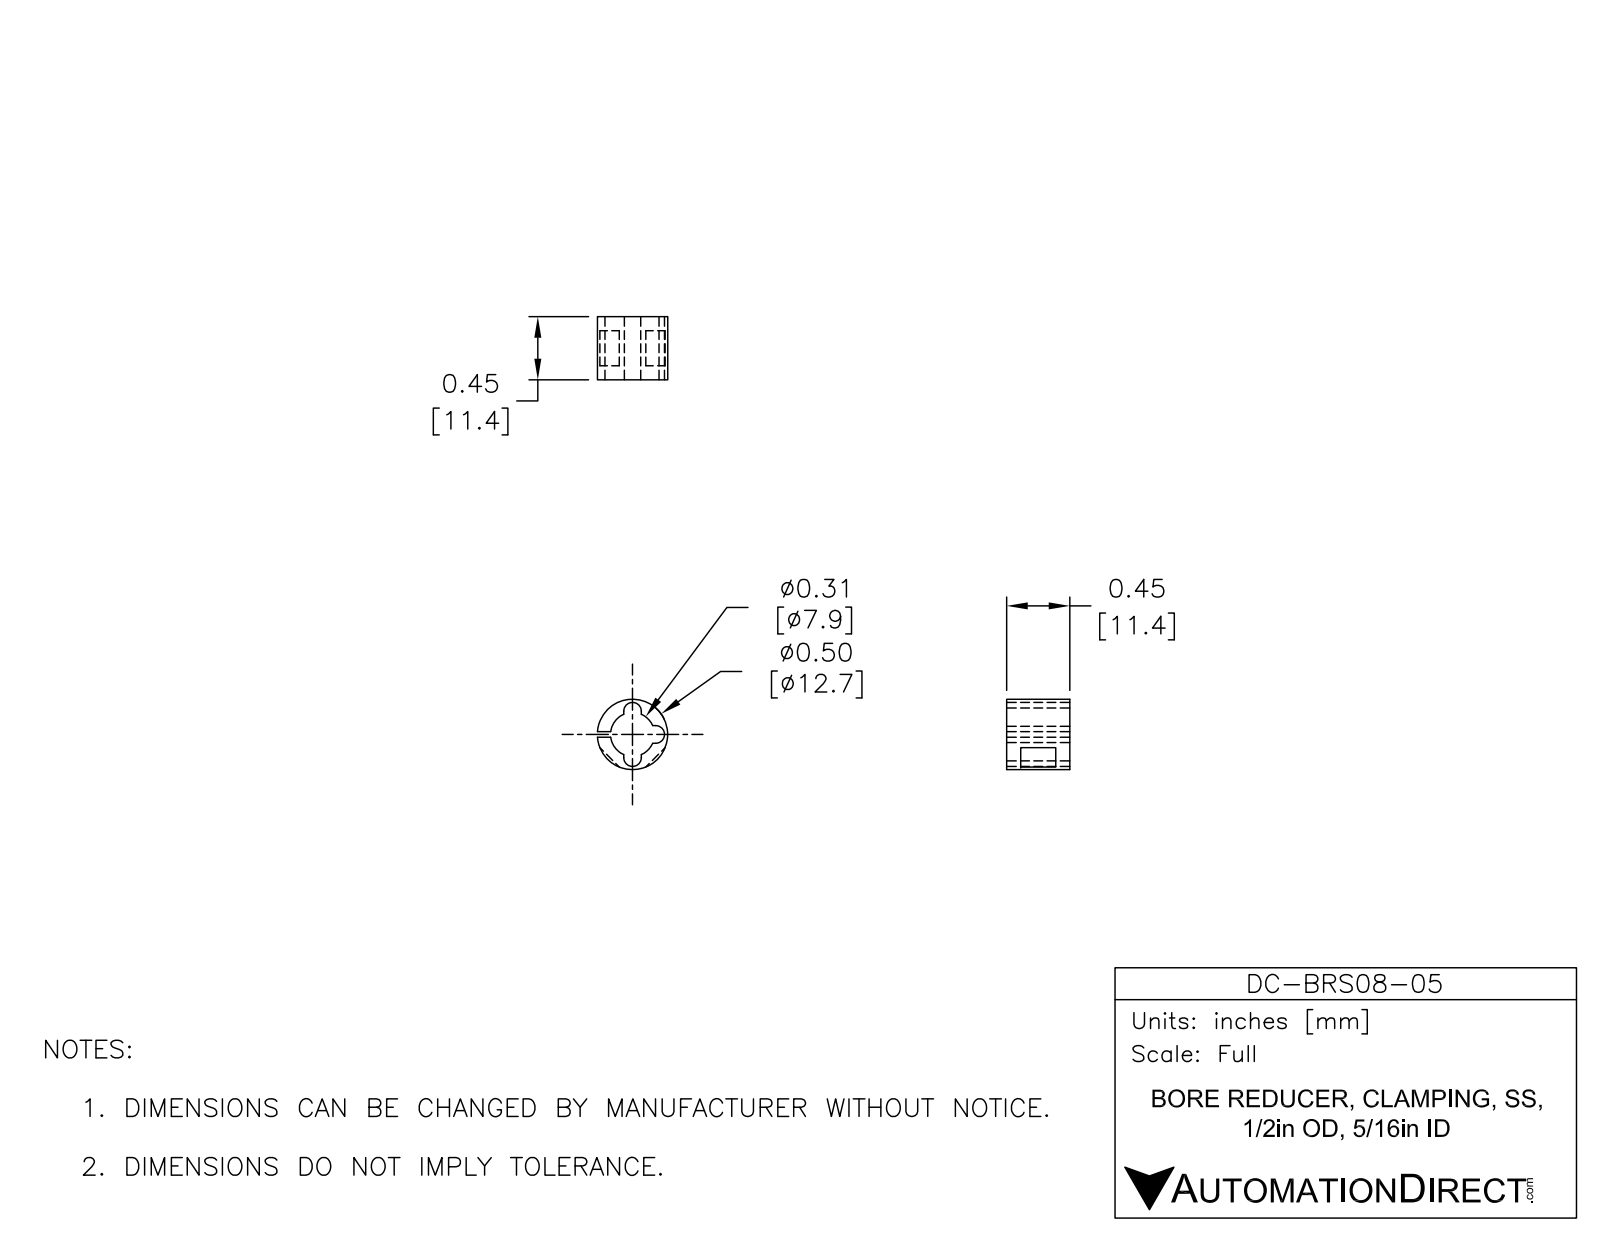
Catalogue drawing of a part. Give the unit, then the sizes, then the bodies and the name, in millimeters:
Units: millimetres
Overall size (bounding box): 12.7 × 12.68 × 11.4
Round bosses / shafts (diameter × count): ⌀12.7 ×1
Partial cylindrical surfaces — rounded edges, fillets, slot ends (radius × count): R1.59 ×3, R3.97 ×1
Main face-to-face distances: 11.4, 1.02, 3.18, 1.08, 2.1, 2.54, 8.86, 6.32
Volume: 660 mm³ · Surface area: 992 mm²
Bodies: 1 solid, 27 faces (16 planar, 11 cylindrical, 0 other)
Part name (STEP PRODUCT): DC-BRS08-05
STEP written by: SolidWorks 2015 (AUTOMOTIVE_DESIGN)
